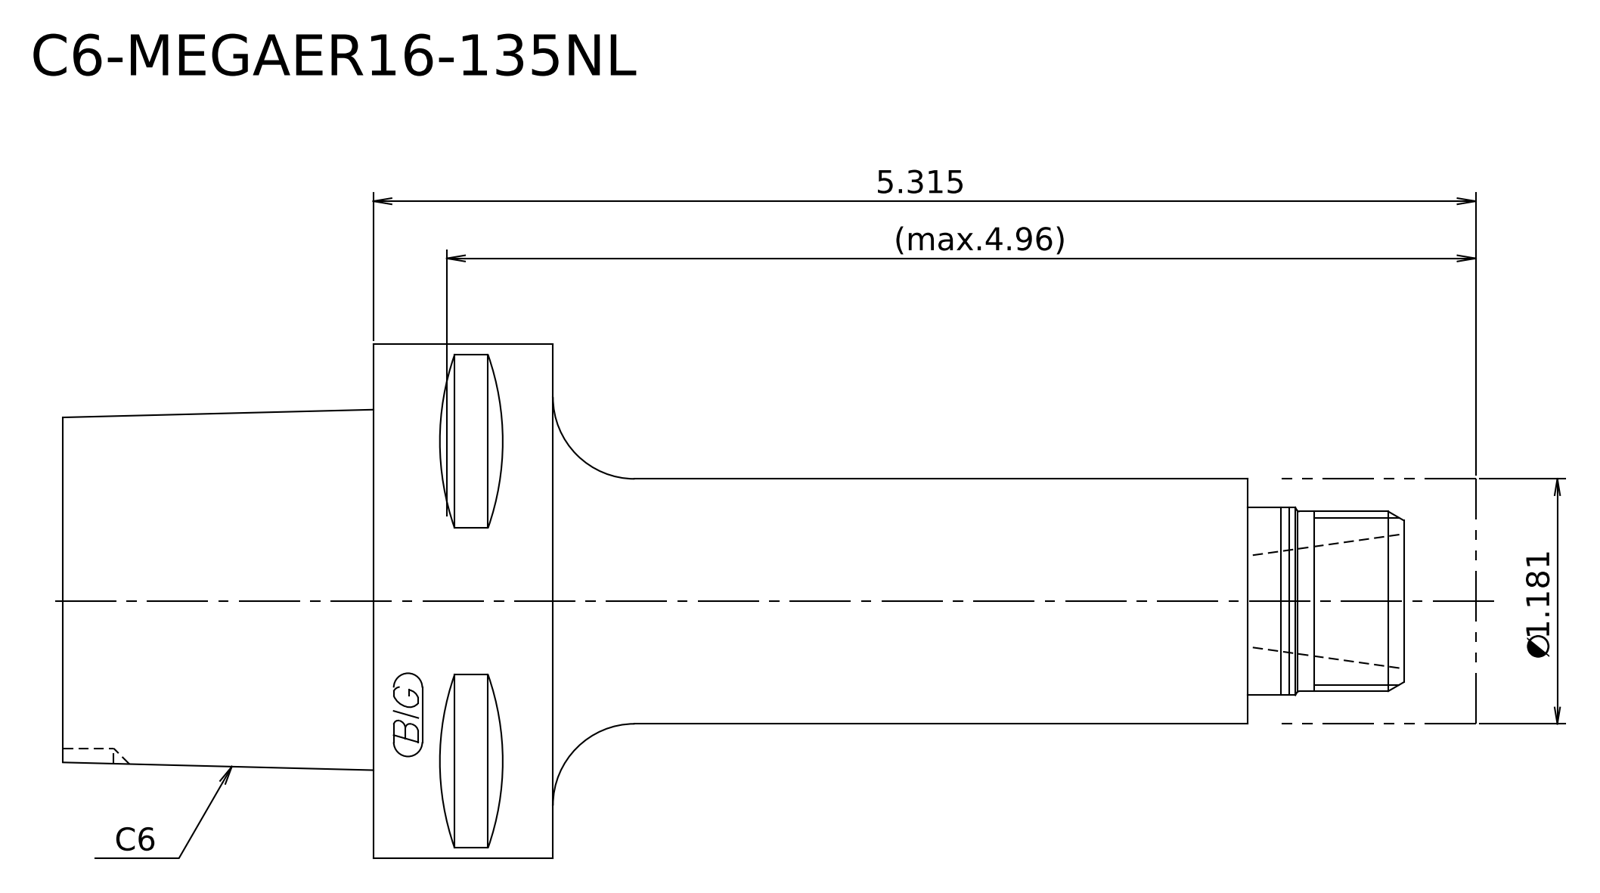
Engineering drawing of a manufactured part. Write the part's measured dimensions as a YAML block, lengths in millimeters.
step_written_by: "Kubotek KeyCreator 2011 V10.0.2 (22737) (automotive_design)"
units: millimeters
bodies: {solids: 2, faces: 18, planar: 7, cylindrical: 5, other: 6}
overall_size: [173, 63, 63]
volume: 214337
surface_area: 28251
round_bosses_or_shafts:
  - {diameter: 63, count: 1}
  - {diameter: 30, count: 1}
  - {diameter: 23, count: 1}
  - {diameter: 22, count: 1}
face_to_face_distances: [38, 22, 60, 88, 110, 148, 25, 113, 135, 173]
